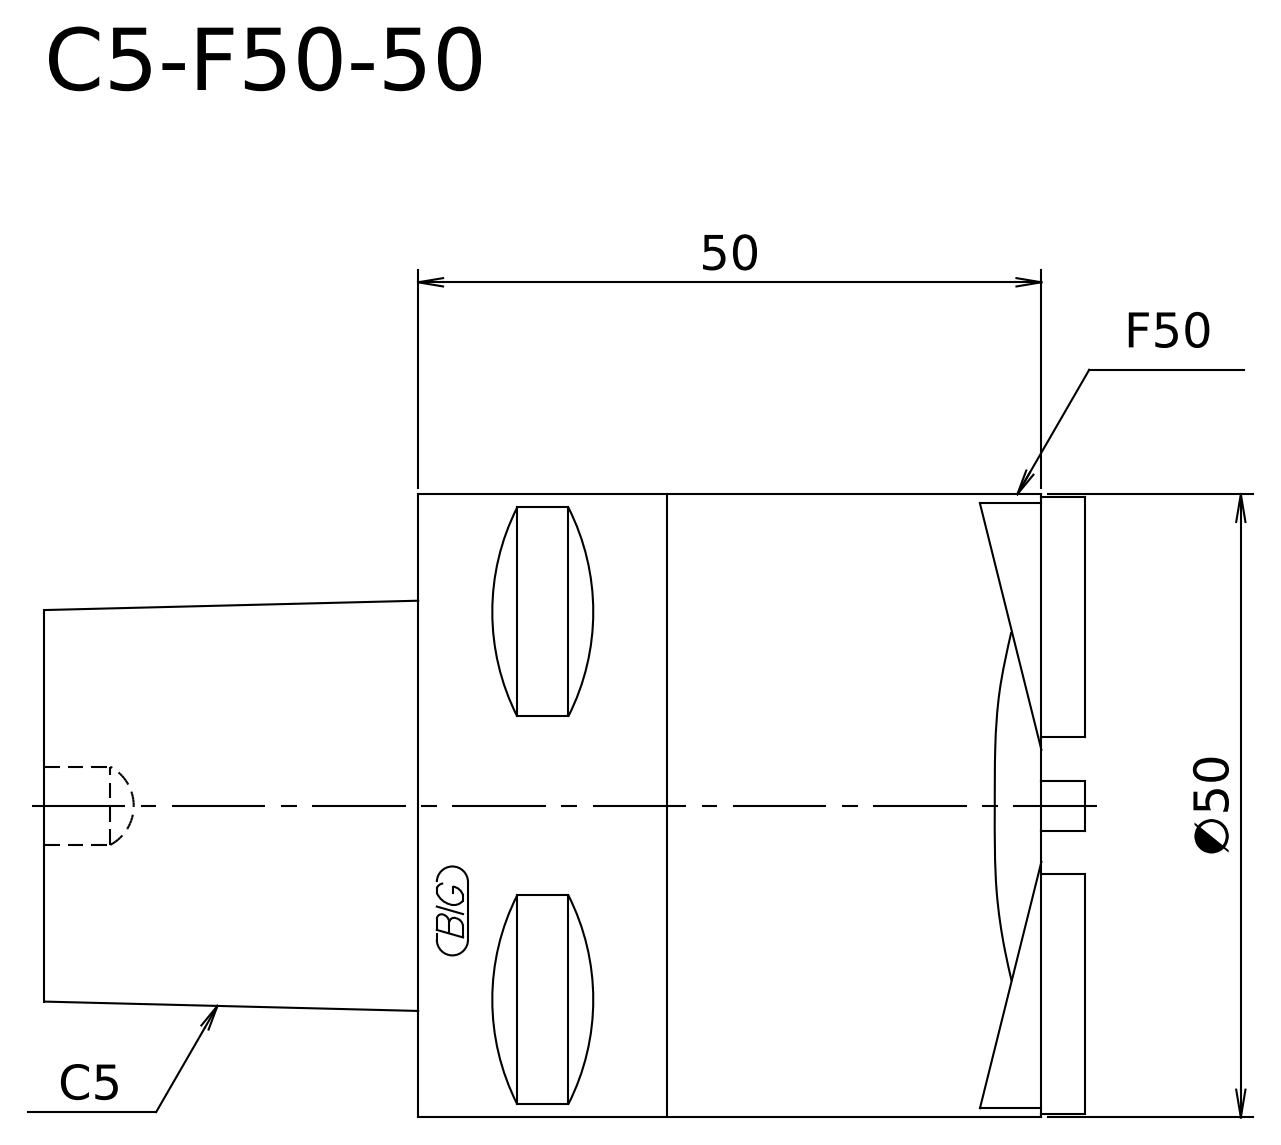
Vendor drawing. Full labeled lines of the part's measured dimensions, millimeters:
Part name (STEP PRODUCT): C5-F50-50
STEP written by: SolidWorks 2021 (CONFIG_CONTROL_DESIGN)
Units: millimetres
Bodies: 1 solid, 7 faces (3 planar, 2 cylindrical, 2 other)
Overall size (bounding box): 80 × 50 × 50
Volume: 122 548 mm³ · Surface area: 14 737 mm²
Round bosses / shafts (diameter × count): ⌀50 ×1
Main face-to-face distances: 50, 30, 80
